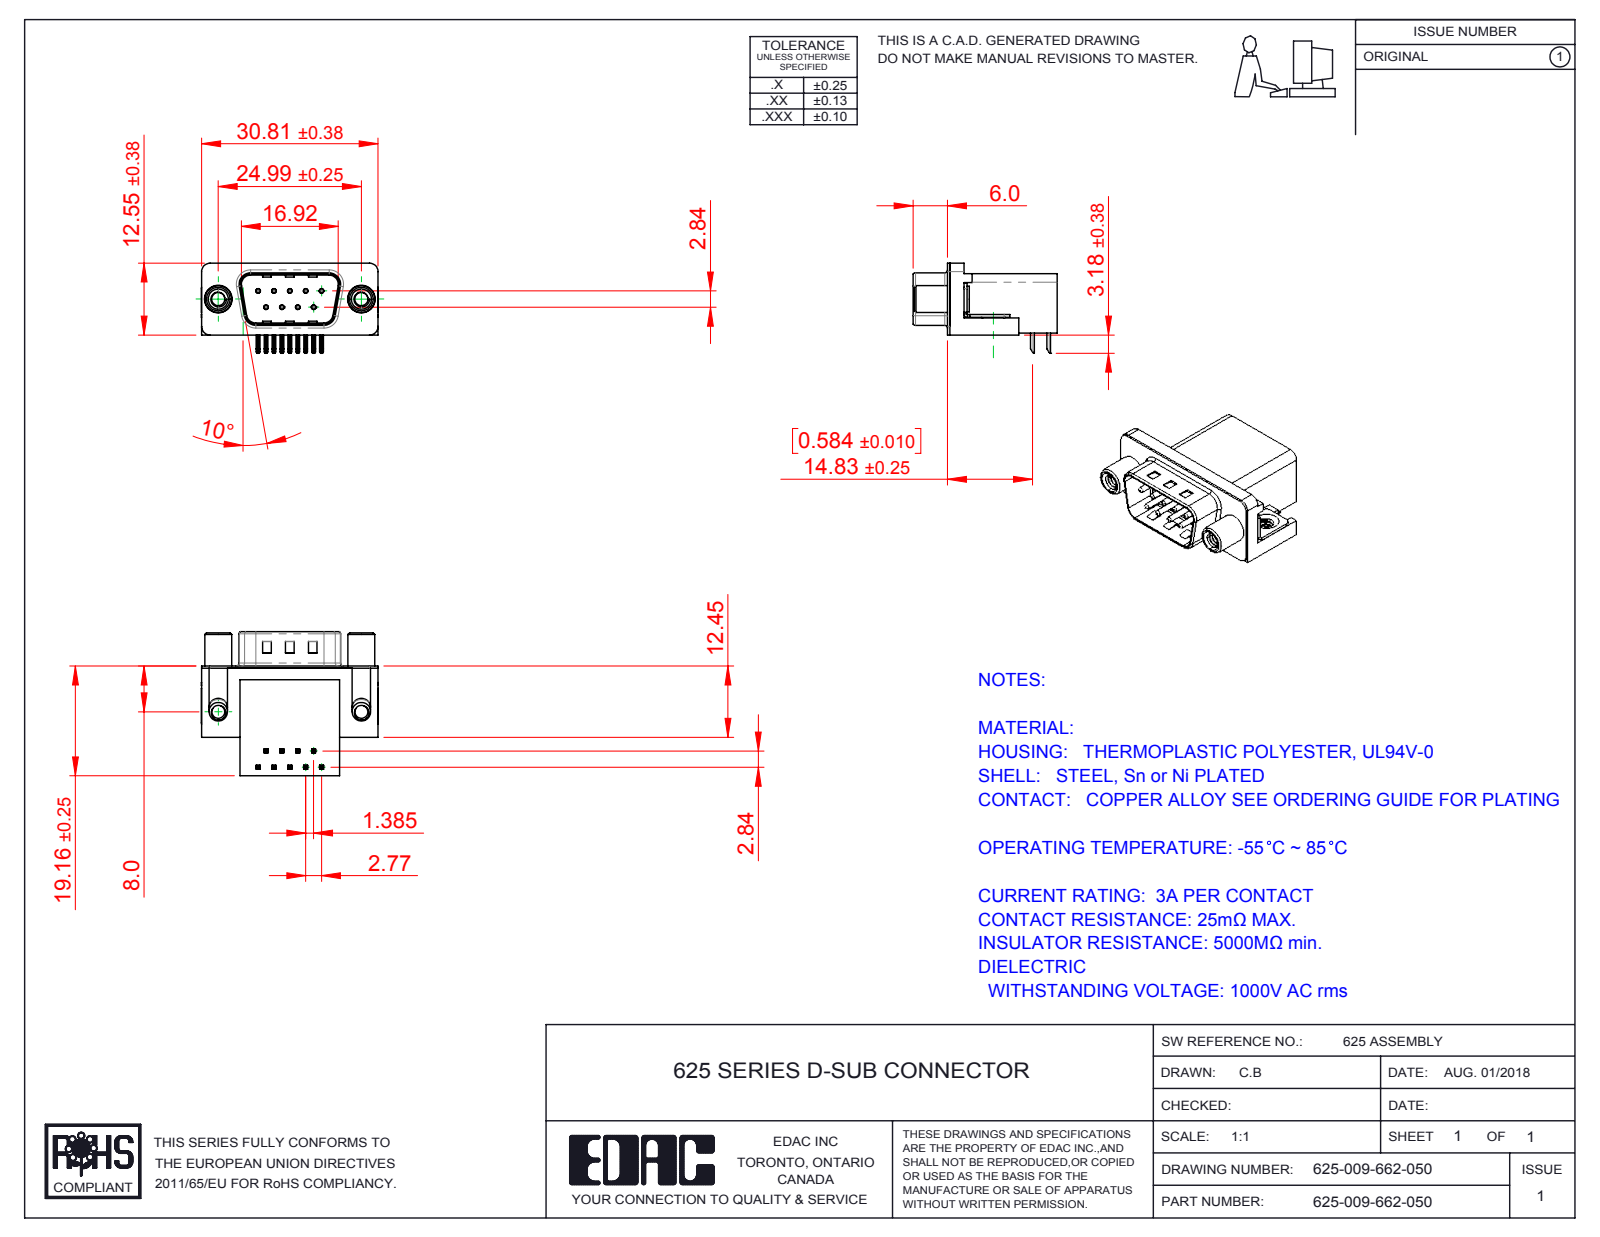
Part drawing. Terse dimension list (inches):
name: 625-009-662-050; 625 4-40 Threaded Board Mount; 625 Round Threaded Standoff; 625 Housing_9 Socket (+3 more)
written by: SolidWorks 2016 (CONFIG_CONTROL_DESIGN)
unit: in
bodies: 15 solids, 1019 faces (567 planar, 337 cylindrical, 115 other)
size: 1.216 × 0.991 × 0.619
volume: 0.279 in³; area: 8.107 in²
holes: 9× ⌀0.014, 9× ⌀0.031, 2× ⌀0.089, 2× ⌀0.091, 2× ⌀0.122, 2× ⌀0.157, 2× ⌀0.189, 2× ⌀0.197
bosses: 9× ⌀0.03, 2× ⌀0.193, 2× ⌀0.185, 2× ⌀0.177, 2× ⌀0.152, 2× ⌀0.128
rounds: 36× R0.01, 18× R0.005, 16× R0.039, 9× R0.02, 8× R0.059, 8× R0.063, 4× R0.035, 4× R0.079
face distances: 0.016, 0.407, 0.739, 0.754, 0.64, 0.098, 0.114, 0.014, 0.421, 0.264
hole spacings: 0.124, 0.109, 0.218, 0.198, 0.198, 0.327, 0.294, 0.295
